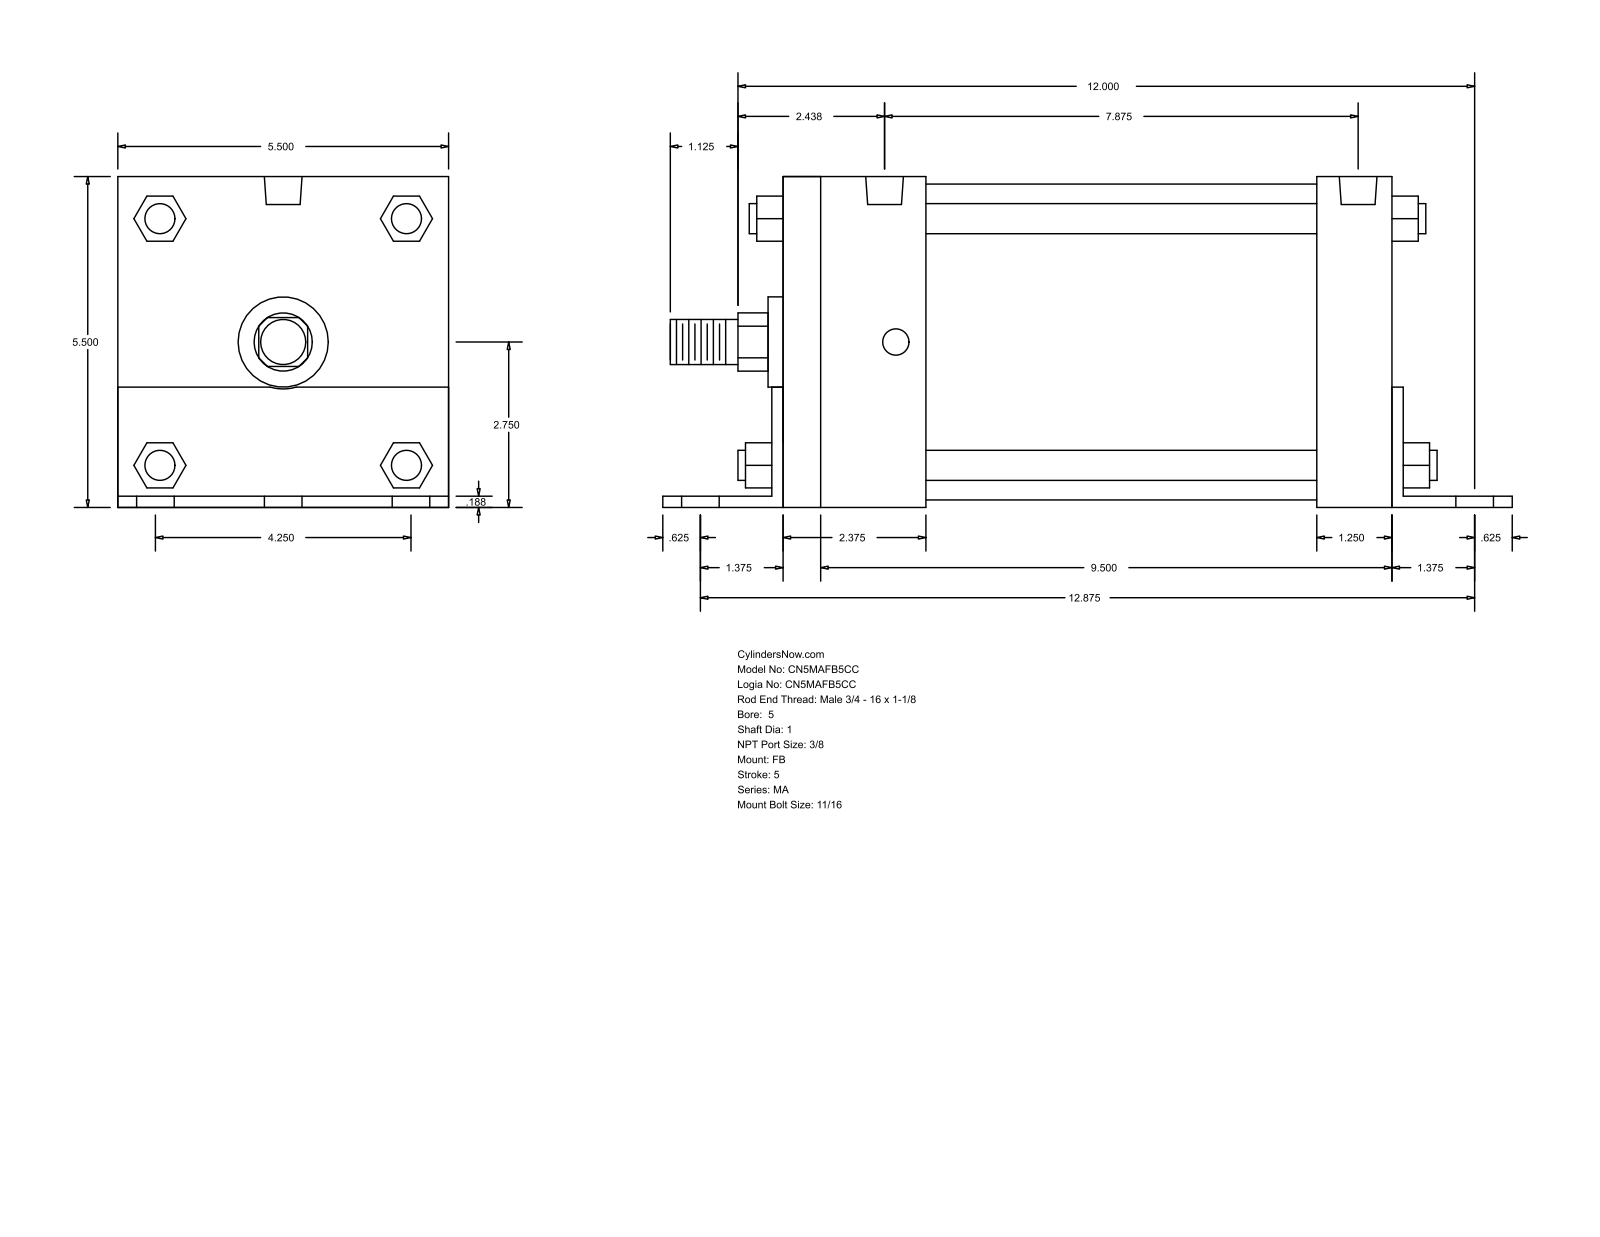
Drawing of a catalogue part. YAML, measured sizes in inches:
part_name: "MA_FB__0500_1"
step_written_by: "GSSL Pune (CONFIG_CONTROL_DESIGN)"
units: inches
bodies: {solids: 0, faces: 140, planar: 105, cylindrical: 35, other: 0}
overall_size: [14.125, 5.502, 5.5]
round_holes:
  - {diameter: 0.687, count: 6}
  - {diameter: 0.437, count: 4}
  - {diameter: 0.627, count: 2}
round_bosses_or_shafts:
  - {diameter: 0.5, count: 4}
  - {diameter: 5.25, count: 1}
  - {diameter: 1.5, count: 1}
  - {diameter: 1, count: 1}
  - {diameter: 0.75, count: 1}
partial_cylinders:
  - {radius: 0.484, count: 1}
  - {radius: 0.78, count: 1}
face_to_face_distances: [5.5, 0.187, 5.502, 10.313, 0.185, 5.315, 10.125, 10.5, 2.563, 2.375]
hole_center_spacings: [2.125, 13.05, 12.875, 0.187, 2.876, 3.005, 3.728, 3.883]
